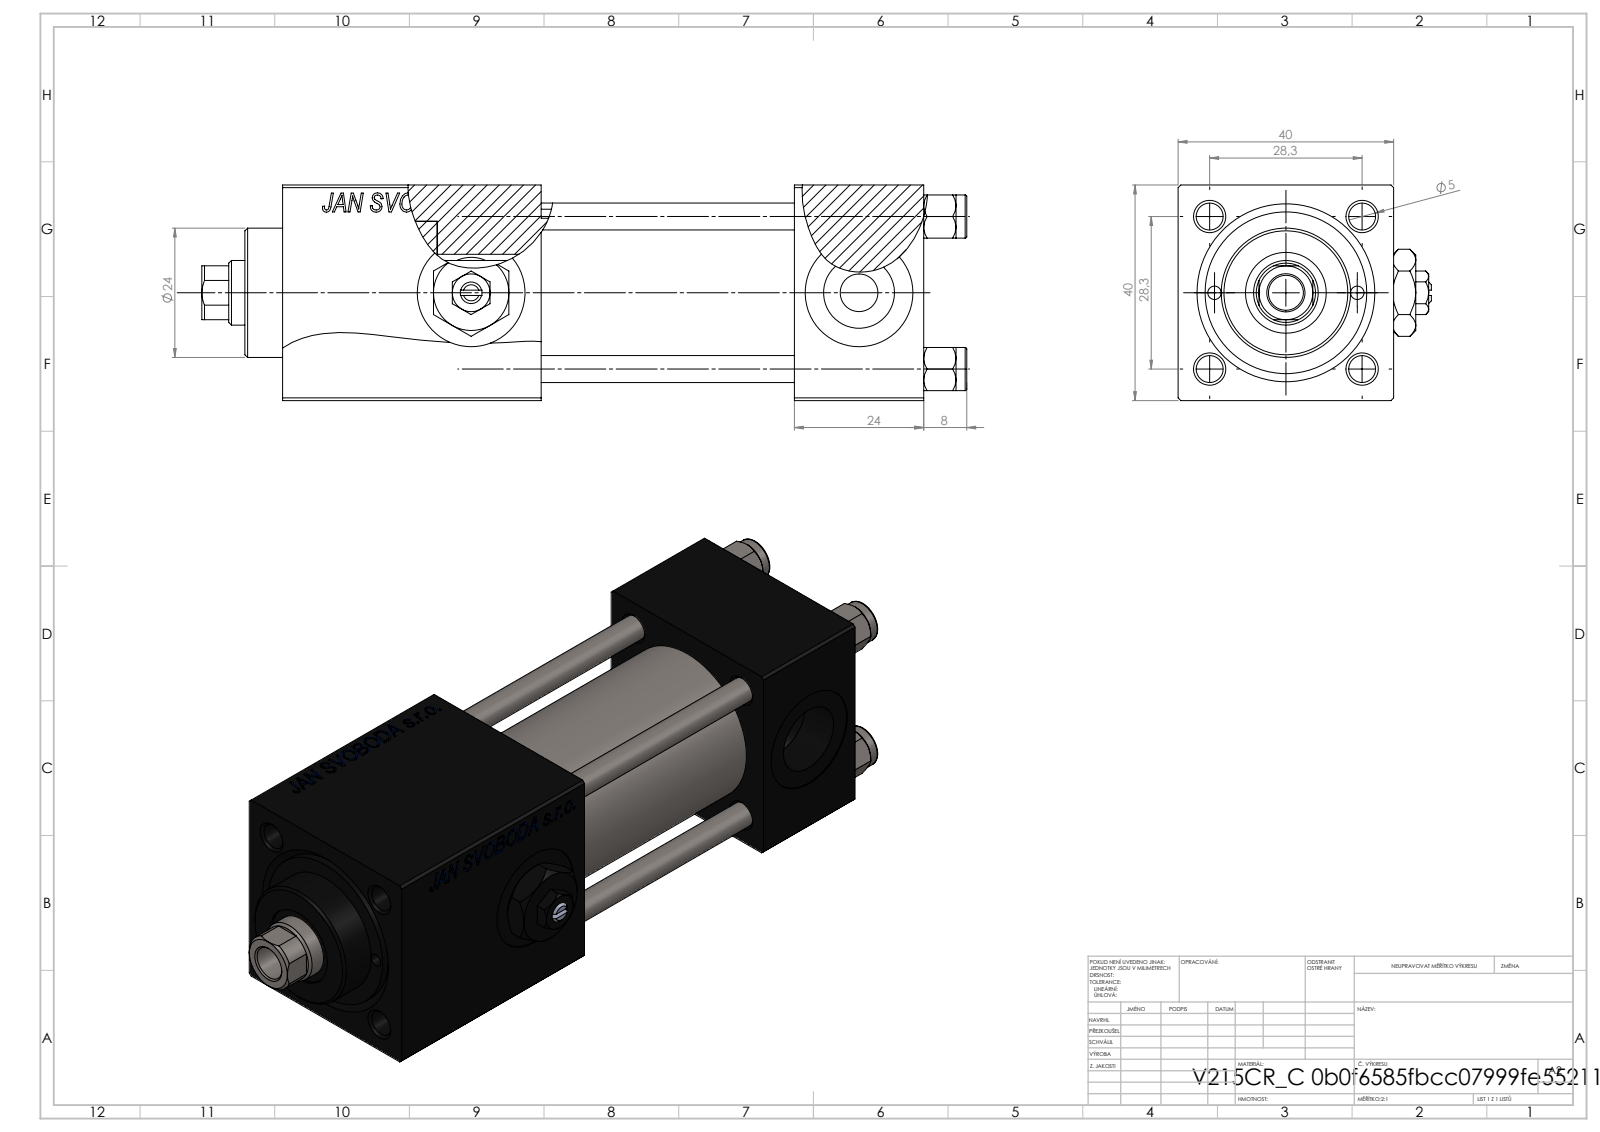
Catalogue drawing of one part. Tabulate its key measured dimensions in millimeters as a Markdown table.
| quantity | value |
| --- | --- |
| part name | V215_VC_A; NUT_M5_C; V215CR_C_Body; V215CR_VCP_C (+2 more) |
| STEP written by | SolidWorks 2019 (CONFIG_CONTROL_DESIGN) |
| units | millimeters |
| bodies | 12 solids, 1201 faces (551 planar, 94 cylindrical, 556 other) |
| overall size | 142 × 47 × 40 |
| volume | 141 941 mm³ |
| surface area | 55 199 mm² |
| round holes (diameter × count) | 5 × 4, 20 × 3, 2.5 × 2, 7 × 2, 13.16 × 2, 6.5 × 1, 12 × 1, 15 × 1, 25 × 1, 30 × 1 |
| round bosses / shafts (diameter × count) | 8 × 4, 31 × 1, 24 × 1 |
| partial cylindrical surfaces (radius × count) | 5.5 × 1 |
| main face-to-face distances | 40, 24, 90.3, 66.3, 48, 47, 71, 19.3, 119, 95 |
| hole center spacings | 14.18, 20.01, 28.3, 30.84, 13.25, 40.02, 26.5, 72 |
